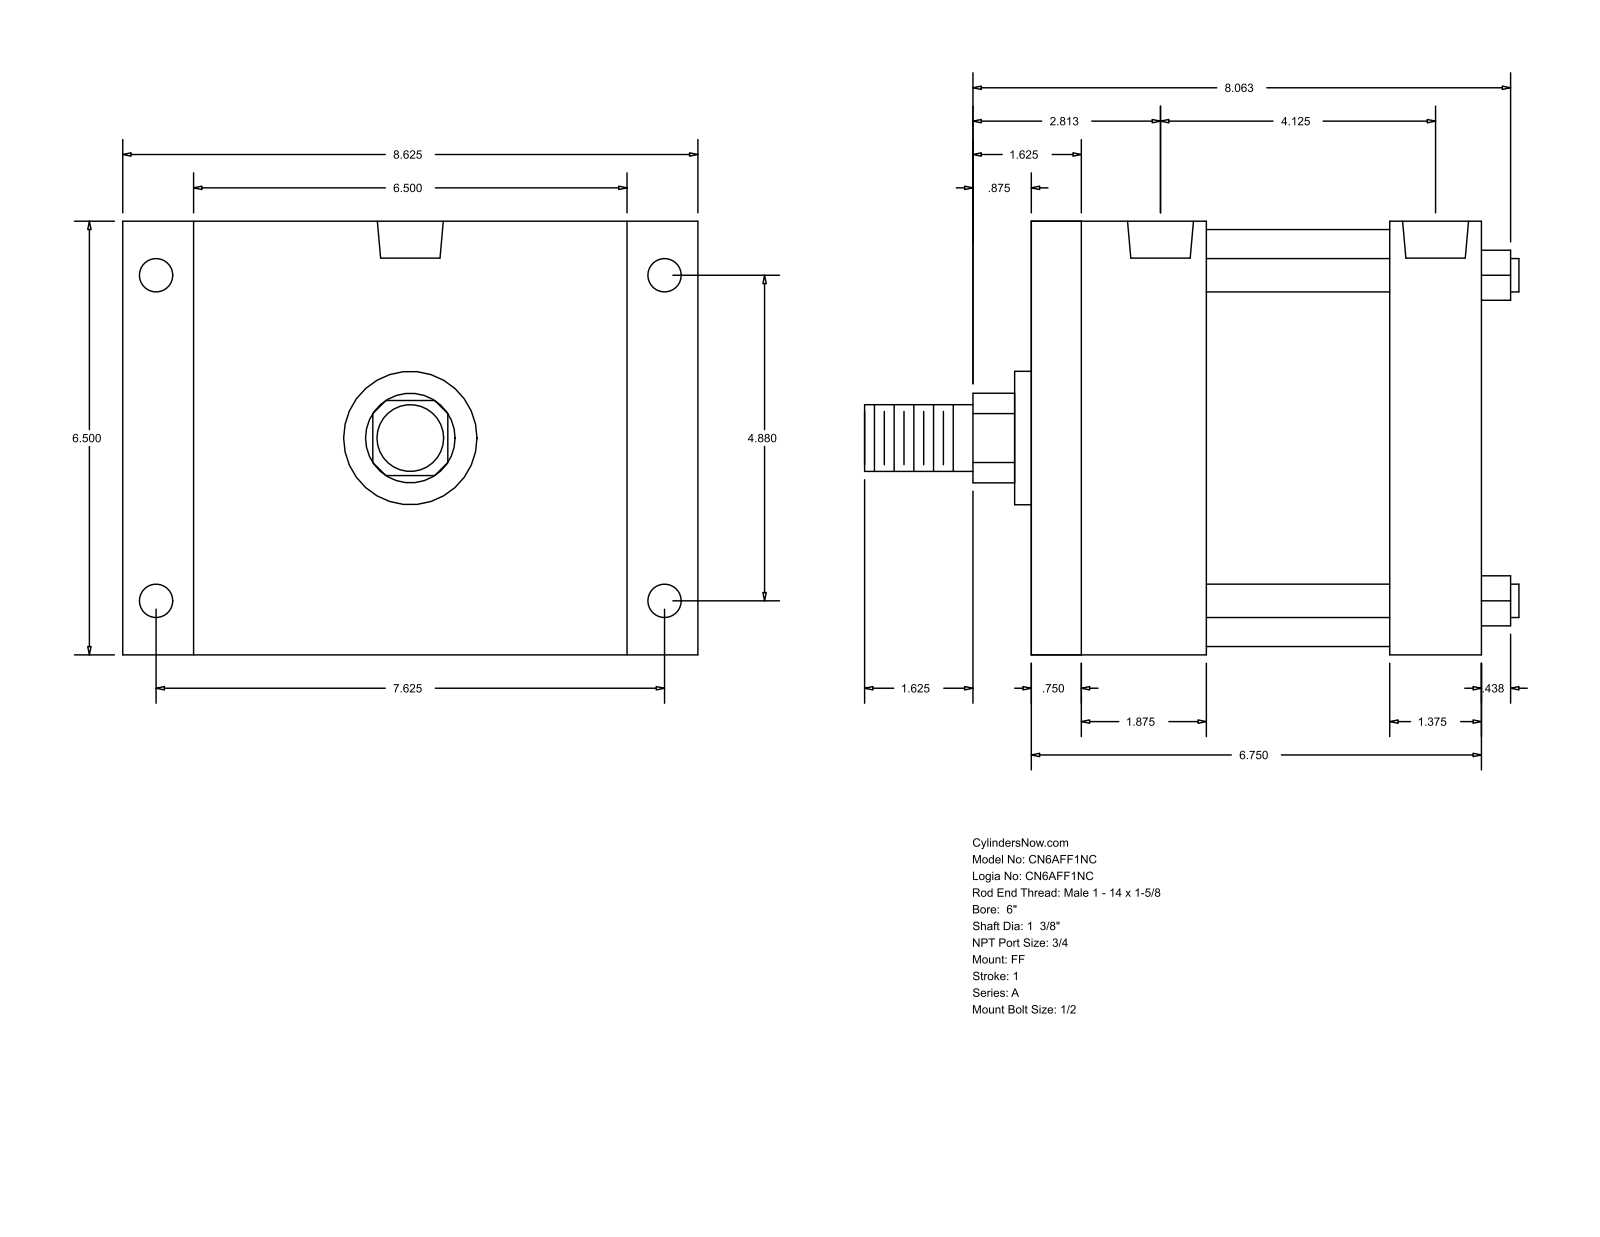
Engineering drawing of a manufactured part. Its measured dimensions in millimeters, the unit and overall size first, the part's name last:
Units: millimetres
Overall size (bounding box): 249.24 × 219.07 × 165.1
Round holes (diameter × count): ⌀12.7 ×4, ⌀15.08 ×4, ⌀25.12 ×2
Round bosses / shafts (diameter × count): ⌀12.7 ×4, ⌀158.75 ×1, ⌀50.8 ×1, ⌀34.92 ×1, ⌀25.4 ×1
Partial cylindrical surfaces — rounded edges, fillets, slot ends (radius × count): R17.06 ×1
Main face-to-face distances: 165.1, 171.45, 19.04, 152.41, 66.67, 47.63, 104.78, 136.52, 117.48, 69.85
Hole centre spacings: 5.56, 93.65, 99.21, 123.96, 193.68, 229.95, 104.77
Bodies: 0 solids, 92 faces (64 planar, 28 cylindrical, 0 other)
Part name (STEP PRODUCT): A_FF__0600_1.375
STEP written by: GSSL Pune (CONFIG_CONTROL_DESIGN)
